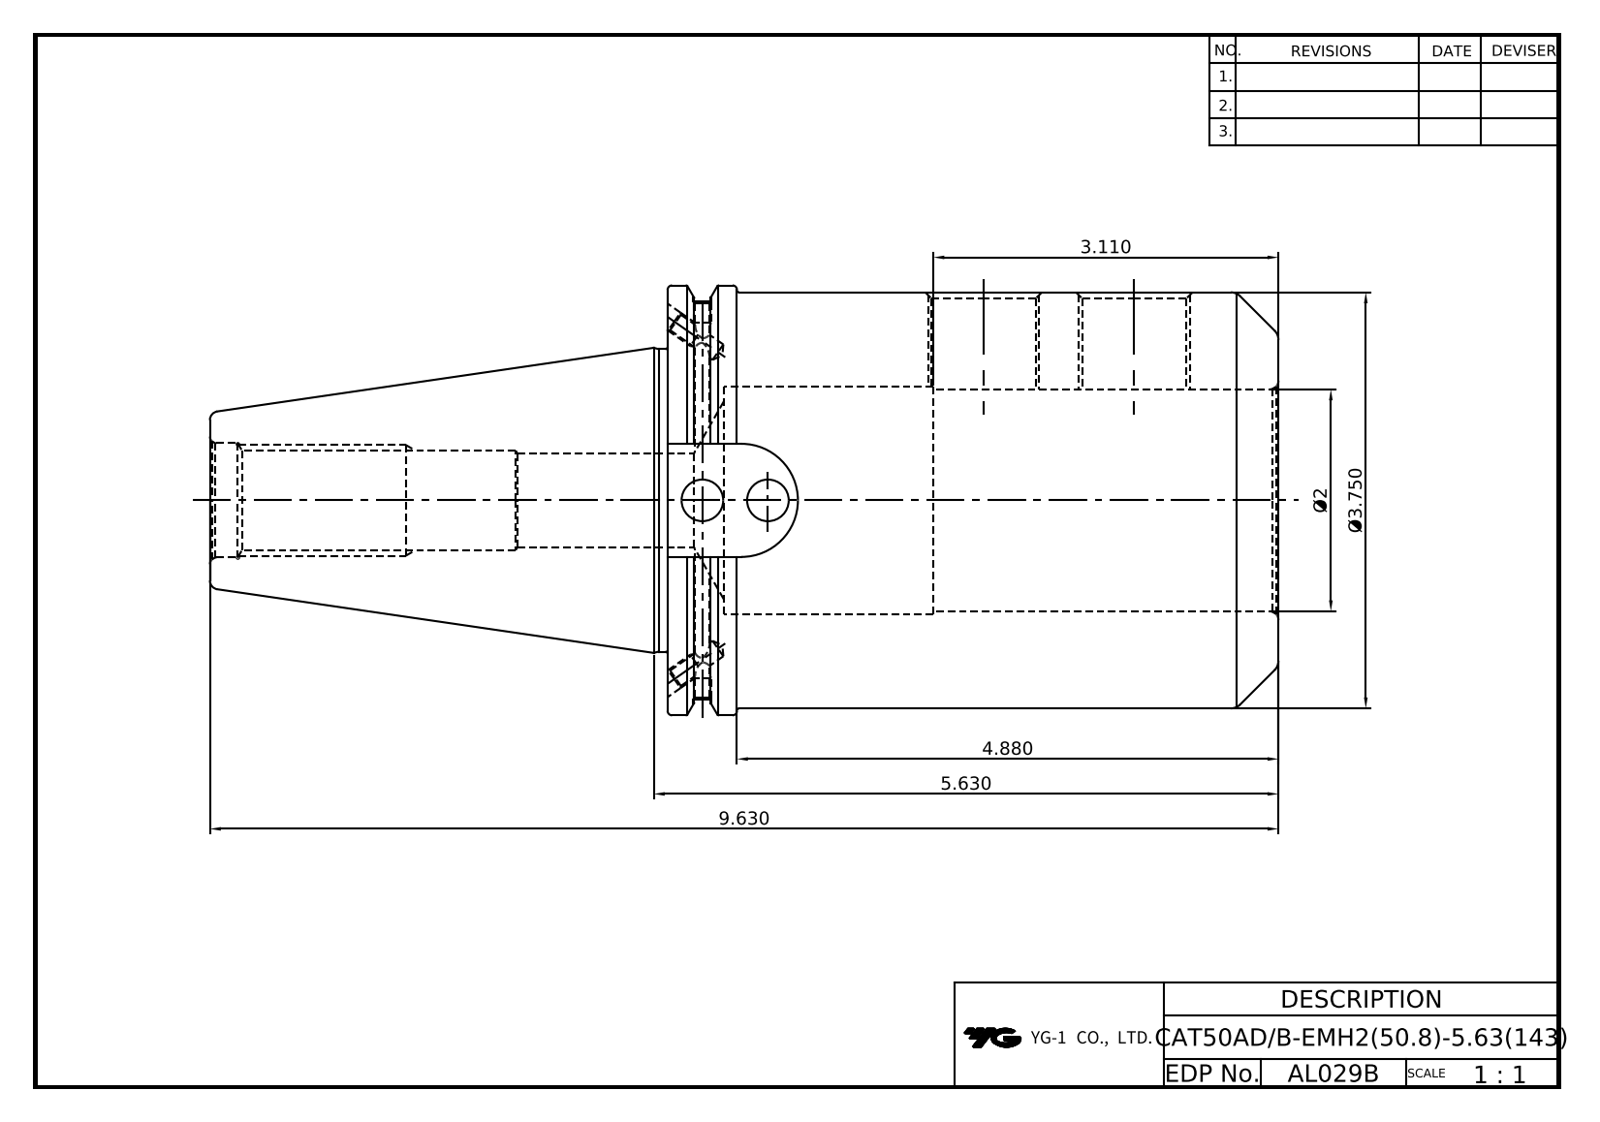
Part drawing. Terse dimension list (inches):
name: CAT50ADB-EMH50.8-143
written by: Autodesk Inventor 2024 (AUTOMOTIVE_DESIGN)
unit: in
bodies: 1 solid, 91 faces (34 planar, 30 cylindrical, 27 other)
size: 9.63 × 3.875 × 3.75
volume: 55.04 in³; area: 159.7 in²
holes: 2× ⌀0.128, 2× ⌀0.163, 2× ⌀0.165, 2× ⌀0.197, 2× ⌀0.923, 1× ⌀0.375, 1× ⌀0.846, 1× ⌀0.865, 1× ⌀1.031, 1× ⌀2, 1× ⌀2.047
bosses: 1× ⌀3.875, 1× ⌀3.75, 1× ⌀3.594, 1× ⌀2.726
rounds: 1× R0.51
face distances: 5.505, 0.505, 5, 2.875, 4.125, 4.63, 9.63, 1.02, 4.513, 0.389
hole spacings: 1.358
